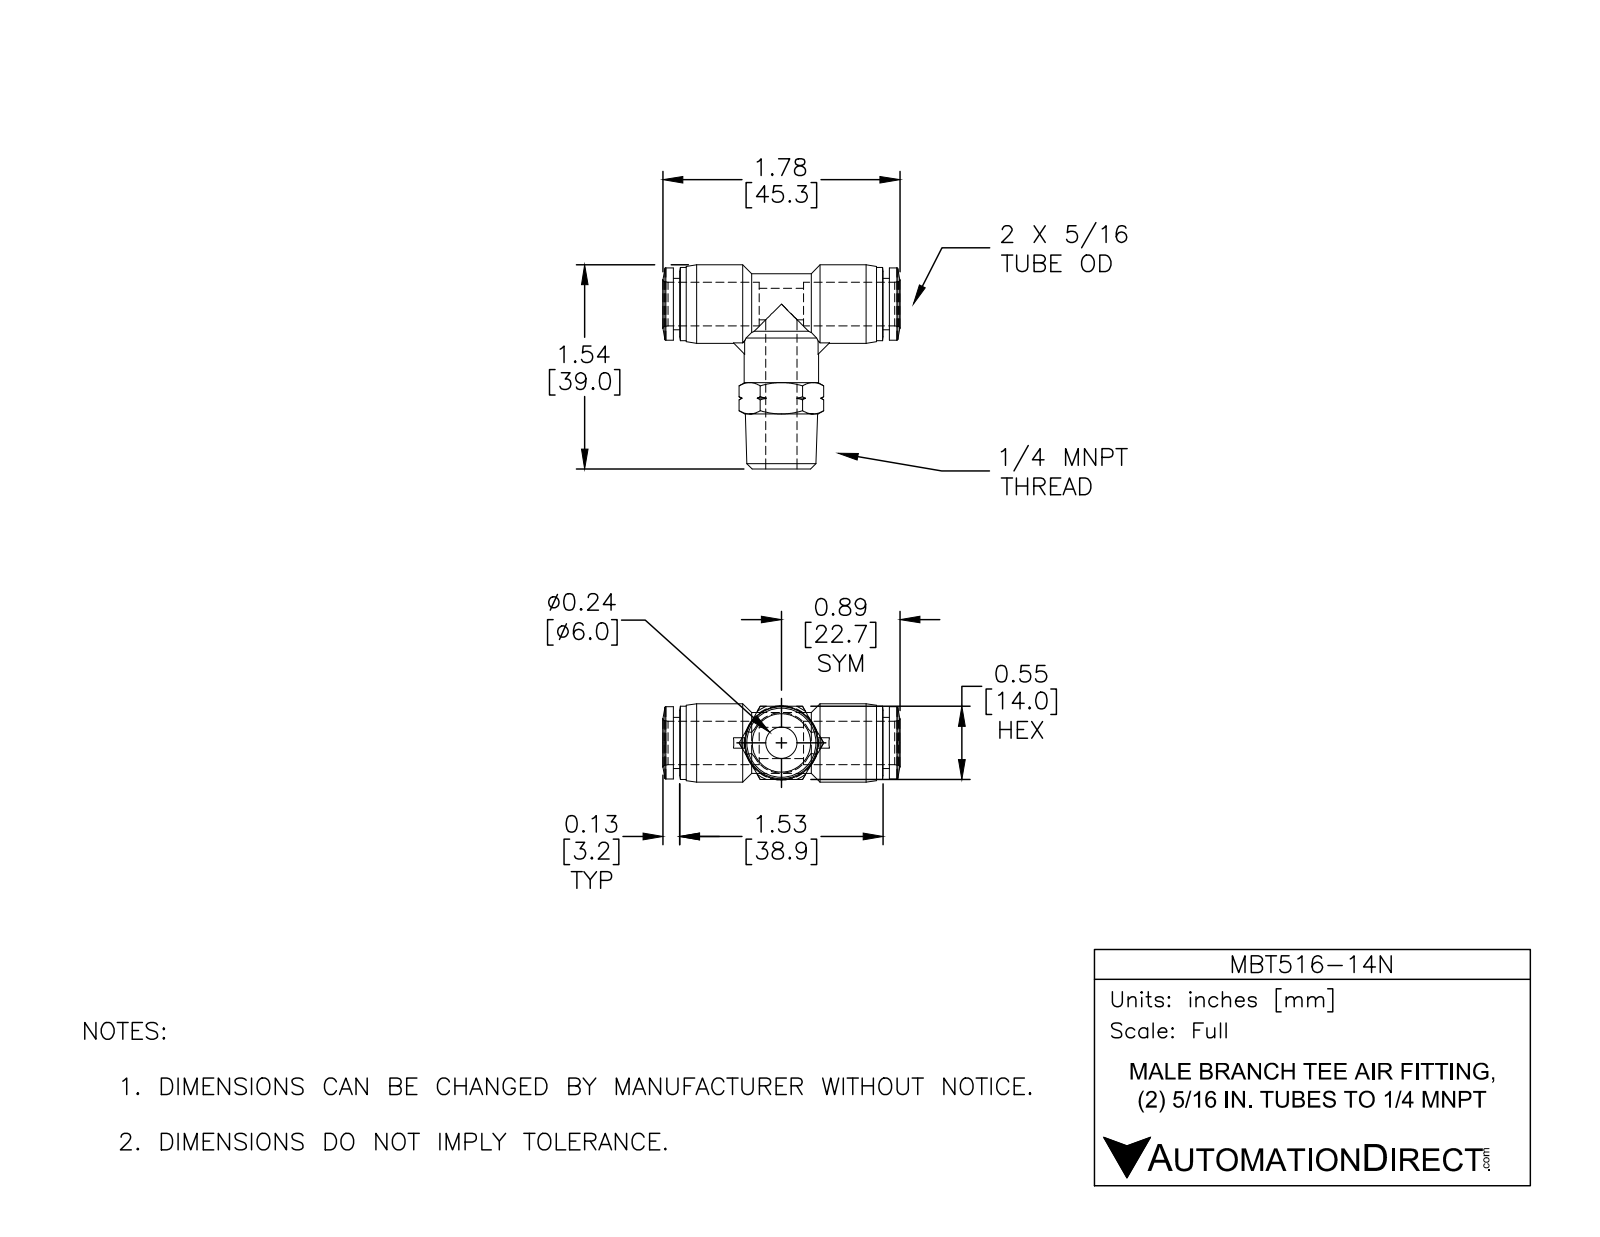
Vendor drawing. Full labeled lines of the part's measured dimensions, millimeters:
Part name (STEP PRODUCT): MBT516-14N
STEP written by: SolidWorks 2015 (AUTOMOTIVE_DESIGN)
Units: millimetres
Bodies: 1 solid, 121 faces (23 planar, 34 cylindrical, 64 other)
Overall size (bounding box): 45.3 × 39 × 15
Volume: 7 570 mm³ · Surface area: 5 327 mm²
Round holes (diameter × count): ⌀6 ×2, ⌀8.3 ×1
Round bosses / shafts (diameter × count): ⌀15 ×1, ⌀14.2 ×1, ⌀14 ×1, ⌀13.8 ×1, ⌀11.6 ×1, ⌀9.8 ×1
Partial cylindrical surfaces — rounded edges, fillets, slot ends (radius × count): R5.8 ×1
Main face-to-face distances: 14, 1.2, 40.1, 41.3, 16.4, 24.9, 15.2, 23.7, 38.9, 8.5
